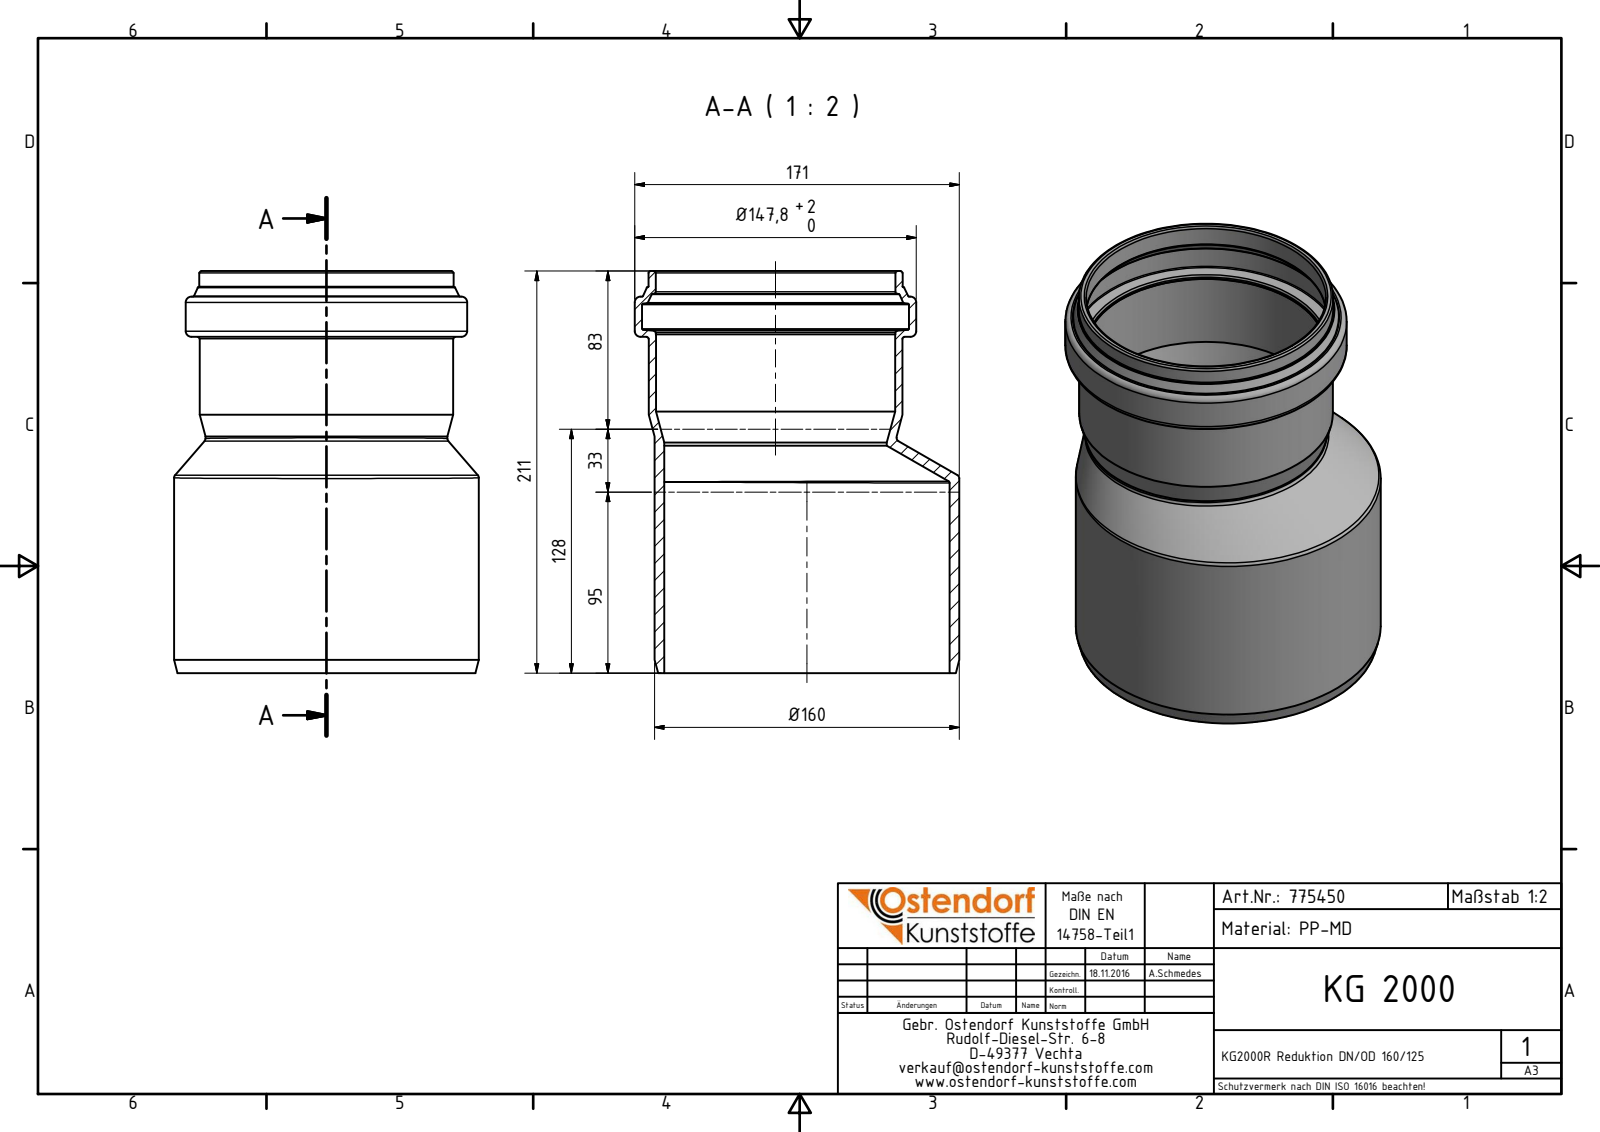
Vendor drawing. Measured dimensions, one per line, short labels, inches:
name: 775450 KG2000R Reduktion DN_OD 160_125
written by: Autodesk Inventor 2016 (AUTOMOTIVE_DESIGN)
unit: in
bodies: 1 solid, 44 faces (5 planar, 11 cylindrical, 28 other)
size: 8.307 × 6.711 × 6.303
volume: 29.01 in³; area: 323.6 in²
holes: 1× ⌀4.602, 1× ⌀4.945, 1× ⌀4.957, 1× ⌀5.52, 1× ⌀5.902
bosses: 1× ⌀6.303, 1× ⌀5.819, 1× ⌀5.256, 1× ⌀5.244, 1× ⌀5.004
face distances: 6.949, 8.307, 1.358, 7.78, 0.831, 0.528, 6.997, 0.048, 0.782, 1.31
hole spacings: 0.65
